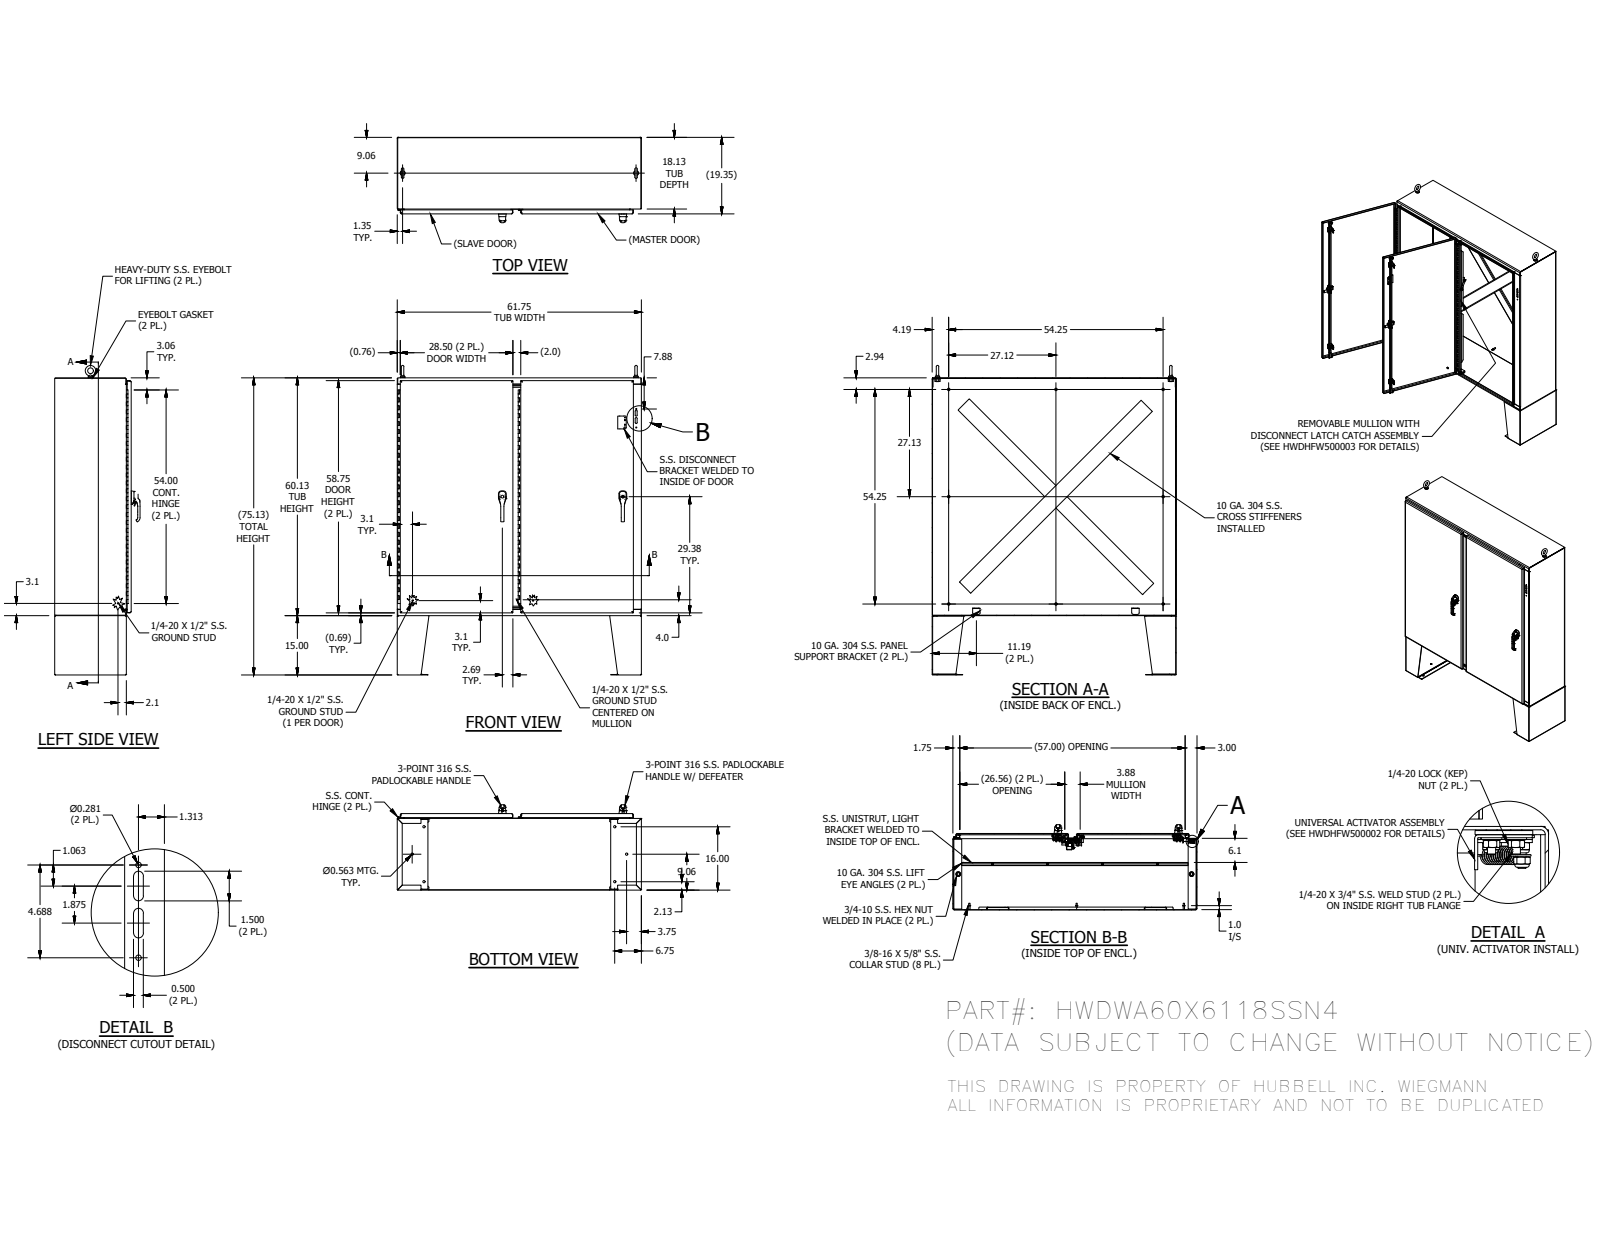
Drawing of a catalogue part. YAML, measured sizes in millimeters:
part_name: "WA60X6118SSN4BLR; WAX6118SSN4TOP; WAX6118SSN4BTM; HFW332010S (+8 more)"
step_written_by: "Autodesk Inventor 2016 (AUTOMOTIVE_DESIGN)"
units: millimeters
bodies: {solids: 220, faces: 9034, planar: 4178, cylindrical: 3056, other: 1800}
overall_size: [1987.49, 1568.45, 548.55]
volume: 27810000
surface_area: 20960000
round_holes:
  - {diameter: 6.35, count: 18}
  - {diameter: 9.52, count: 18}
  - {diameter: 14.29, count: 18}
  - {diameter: 4.76, count: 9}
  - {diameter: 4.83, count: 8}
  - {diameter: 4.98, count: 8}
  - {diameter: 6.65, count: 8}
  - {diameter: 7.33, count: 8}
  - {diameter: 8.51, count: 8}
  - {diameter: 9.65, count: 8}
  - {diameter: 3.96, count: 6}
  - {diameter: 5.4, count: 6}
round_bosses_or_shafts:
  - {diameter: 6.35, count: 20}
  - {diameter: 8.38, count: 18}
  - {diameter: 15.88, count: 13}
  - {diameter: 8.56, count: 12}
  - {diameter: 9.52, count: 11}
  - {diameter: 14.29, count: 9}
  - {diameter: 7.11, count: 8}
  - {diameter: 25.4, count: 6}
partial_cylinders:
  - {radius: 0.5, count: 359}
  - {radius: 0.3, count: 221}
  - {radius: 0.51, count: 192}
  - {radius: 3.17, count: 55}
  - {radius: 0.47, count: 42}
  - {radius: 1.27, count: 28}
  - {radius: 2, count: 28}
  - {radius: 6.35, count: 23}
face_to_face_distances: [2.64, 488.79, 486.15, 491.43, 1524.54, 1565.8, 1521.9, 1563.16, 1527.18, 3.17]
hole_center_spacings: [9.65, 19.31, 30.36, 37.06, 126.05, 127, 173.87, 189.72]
